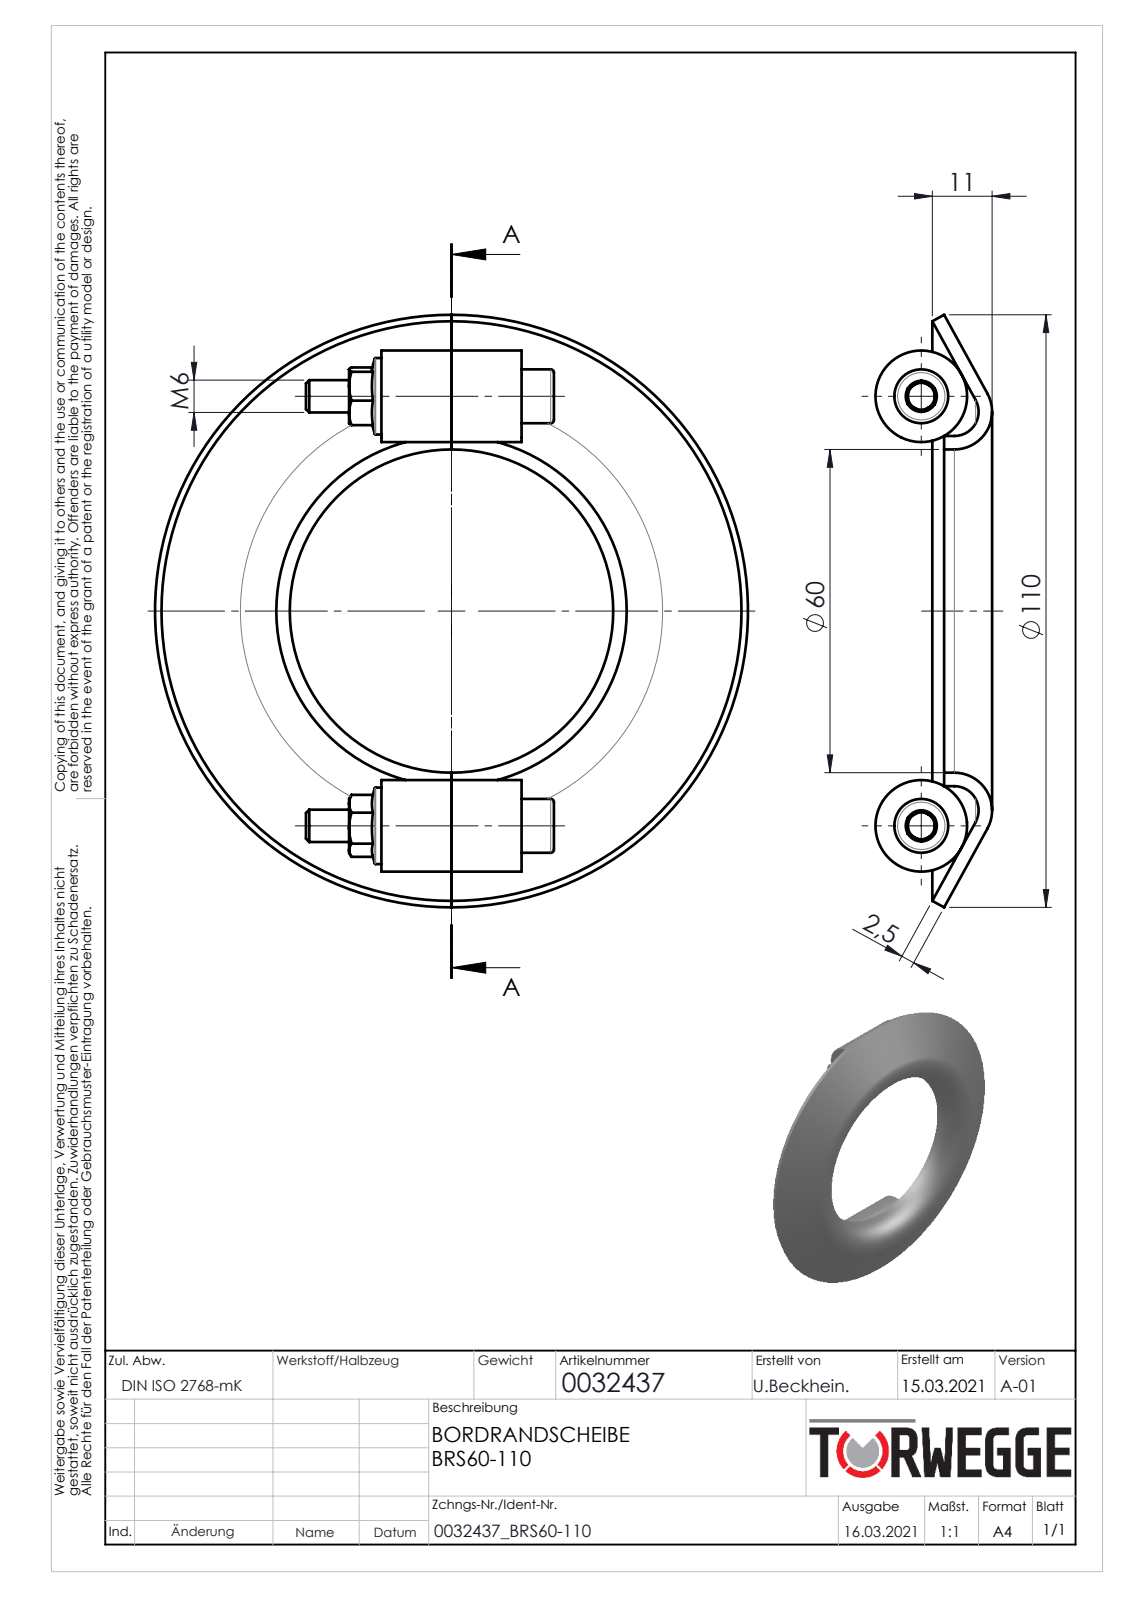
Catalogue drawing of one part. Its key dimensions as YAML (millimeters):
part_name: "0032437"
step_written_by: "SolidWorks 2020 (AUTOMOTIVE_DESIGN)"
units: millimeters
bodies: {solids: 10, faces: 184, planar: 60, cylindrical: 40, other: 84}
overall_size: [110, 110, 21.64]
volume: 33235
surface_area: 26296
round_holes:
  - {diameter: 5, count: 2}
  - {diameter: 7.6, count: 2}
  - {diameter: 60, count: 1}
round_bosses_or_shafts:
  - {diameter: 17, count: 2}
  - {diameter: 14.2, count: 2}
  - {diameter: 10, count: 2}
  - {diameter: 6, count: 2}
  - {diameter: 65, count: 1}
face_to_face_distances: [13, 26, 6, 19, 32, 10, 38, 5, 8, 14]
hole_center_spacings: [79.74]
